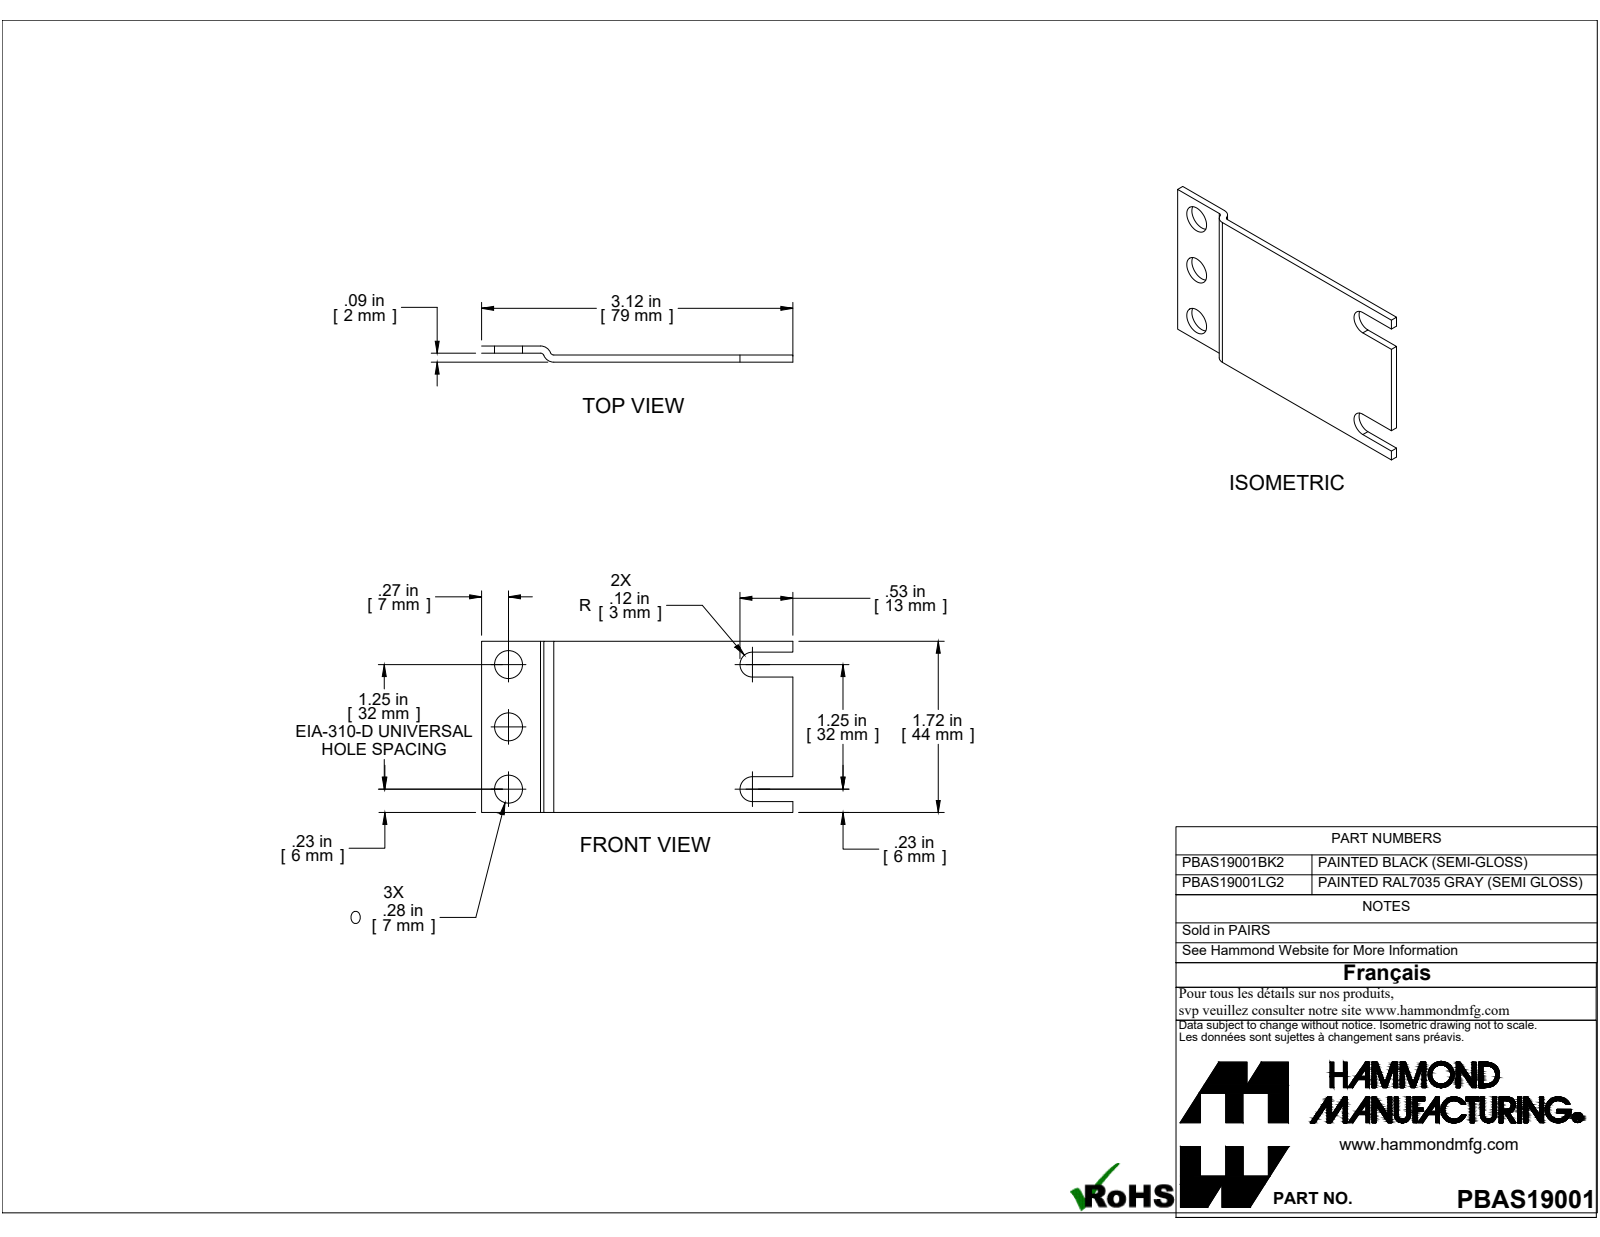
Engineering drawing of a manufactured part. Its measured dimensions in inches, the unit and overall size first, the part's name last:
Units: inches
Overall size (bounding box): 3.125 × 1.718 × 0.162
Round holes (diameter × count): ⌀0.281 ×3
Partial cylindrical surfaces — rounded edges, fillets, slot ends (radius × count): R0.036 ×2, R0.108 ×2, R0.125 ×2
Main face-to-face distances: 0.072, 0.09, 0.162, 0.018, 0.09, 0.072, 1.718, 3.125, 0.109, 1.609
Hole centre spacings: 0.625, 1.25
Volume: 0.36 in³ · Surface area: 11.02 in²
Bodies: 1 solid, 23 faces (14 planar, 9 cylindrical, 0 other)
Part name (STEP PRODUCT): PBAS19001LG2
STEP written by: SolidWorks 2019 (CONFIG_CONTROL_DESIGN)
